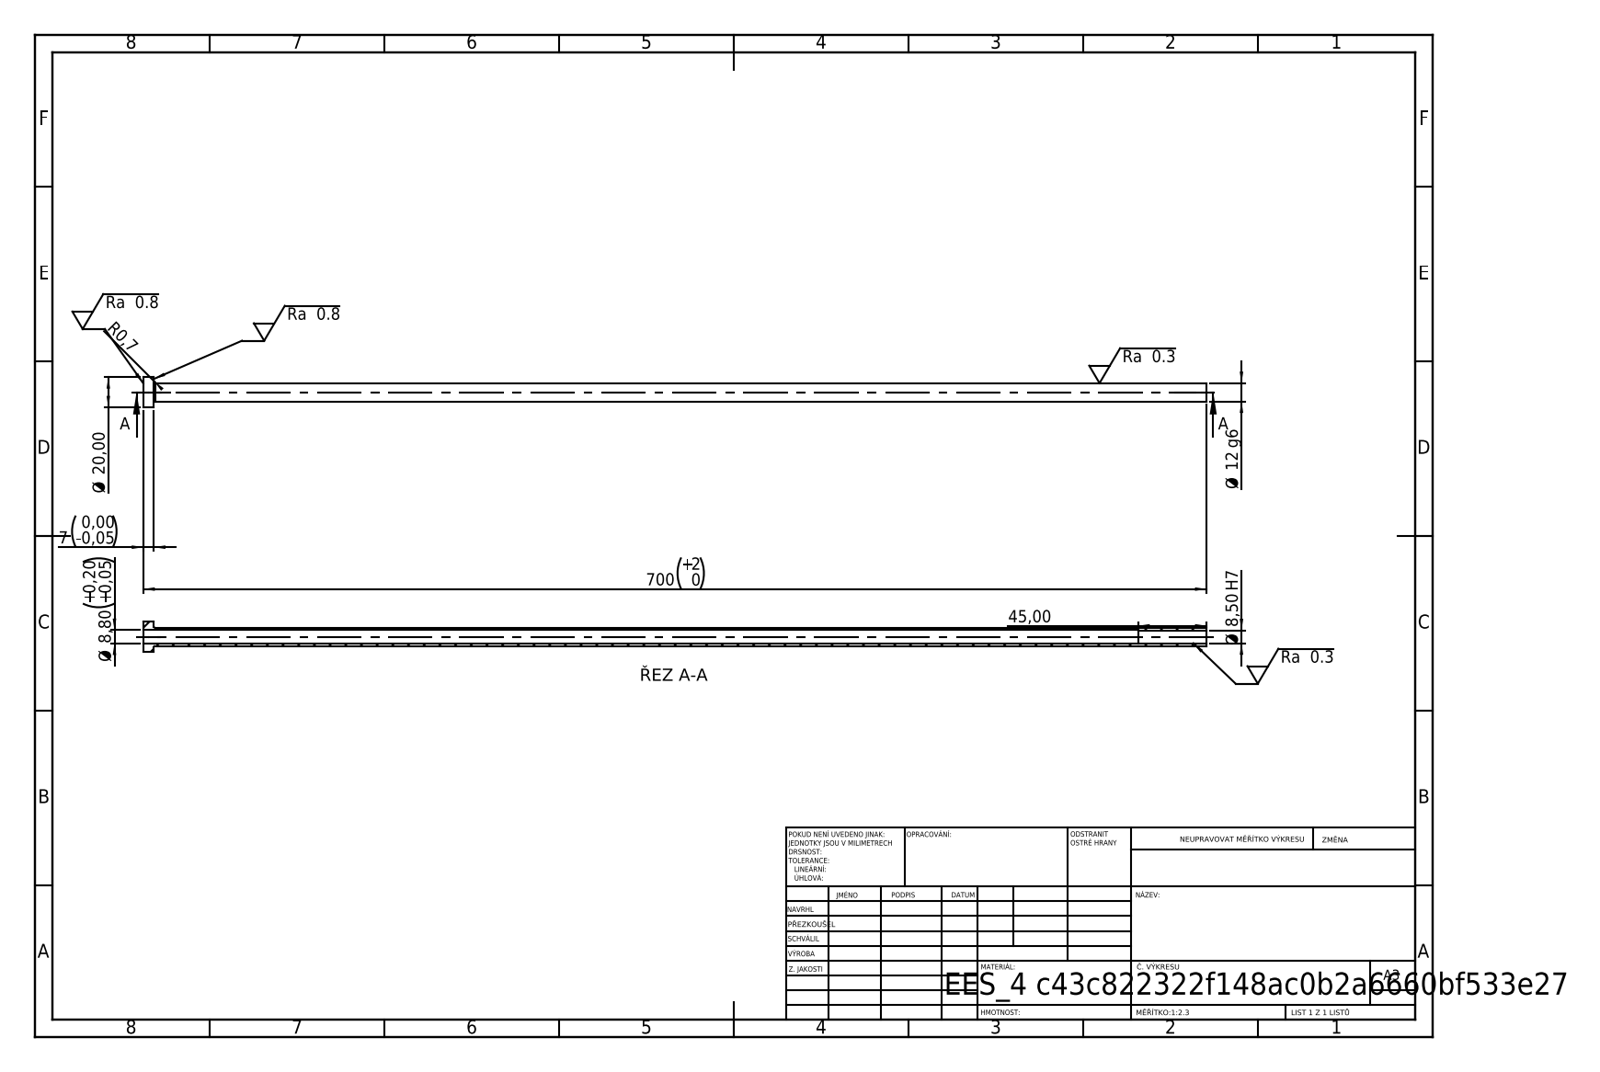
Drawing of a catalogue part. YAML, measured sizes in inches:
step_written_by: "SolidWorks 2019 (CONFIG_CONTROL_DESIGN)"
units: inches
bodies: {solids: 1, faces: 14, planar: 4, cylindrical: 8, other: 2}
overall_size: [27.559, 0.787, 0.787]
volume: 2.33
surface_area: 71.89
round_holes:
  - {diameter: 0.335, count: 1}
  - {diameter: 0.346, count: 1}
round_bosses_or_shafts:
  - {diameter: 0.787, count: 1}
  - {diameter: 0.472, count: 1}
face_to_face_distances: [0.276, 27.559, 27.283, 25.787, 25.512, 1.772]
